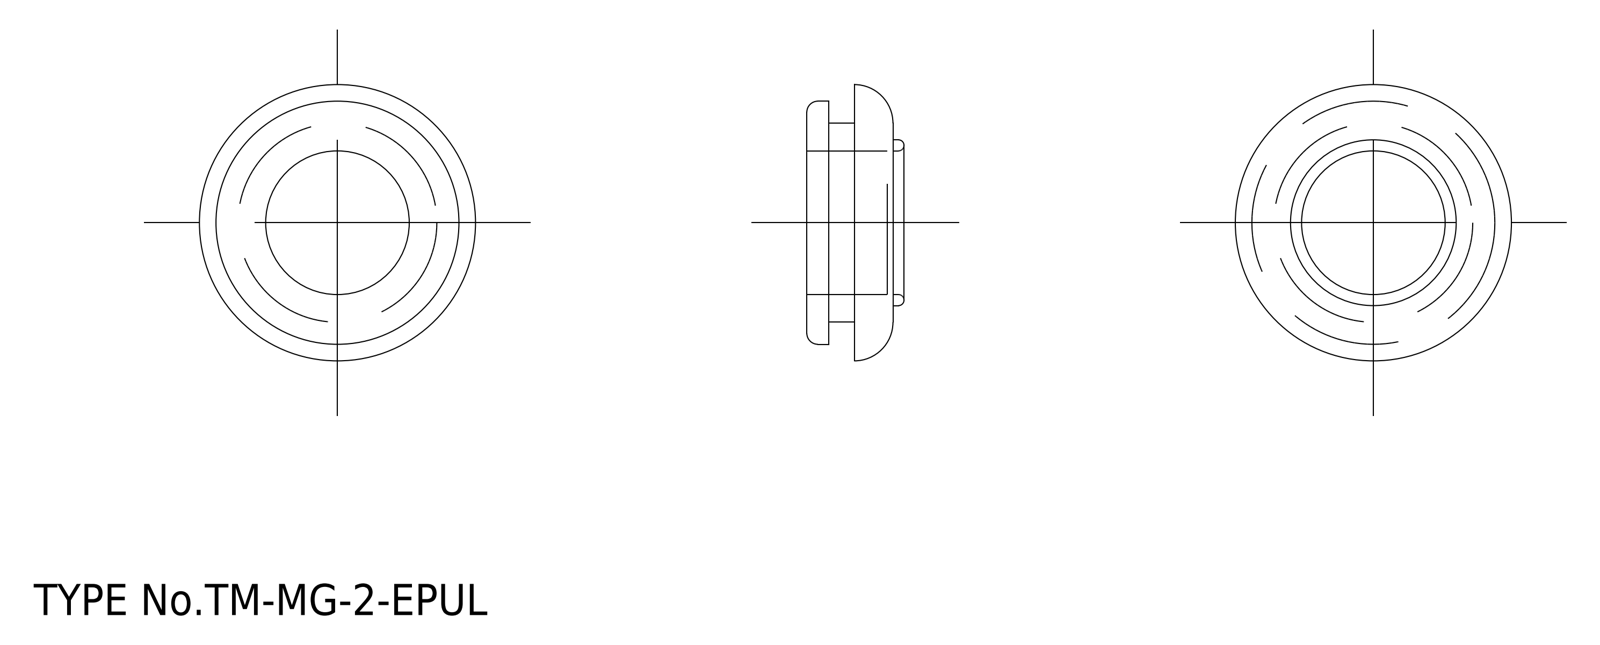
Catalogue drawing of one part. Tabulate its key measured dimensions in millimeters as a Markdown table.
| quantity | value |
| --- | --- |
| STEP written by | spGate 15.6.1 (AUTOMOTIVE_DESIGN) |
| units | millimeters |
| bodies | 1 solid, 22 faces (6 planar, 10 cylindrical, 6 other) |
| overall size | 25 × 25 × 8.8 |
| volume | 1 926 mm³ |
| surface area | 1 990 mm² |
| round holes (diameter × count) | 13 × 1 |
| round bosses / shafts (diameter × count) | 22 × 1, 18 × 1, 15 × 1 |
| main face-to-face distances | 3.5, 4.3, 7.8, 7.3, 3, 0.5, 2, 2.3, 5.3, 5.8 |
